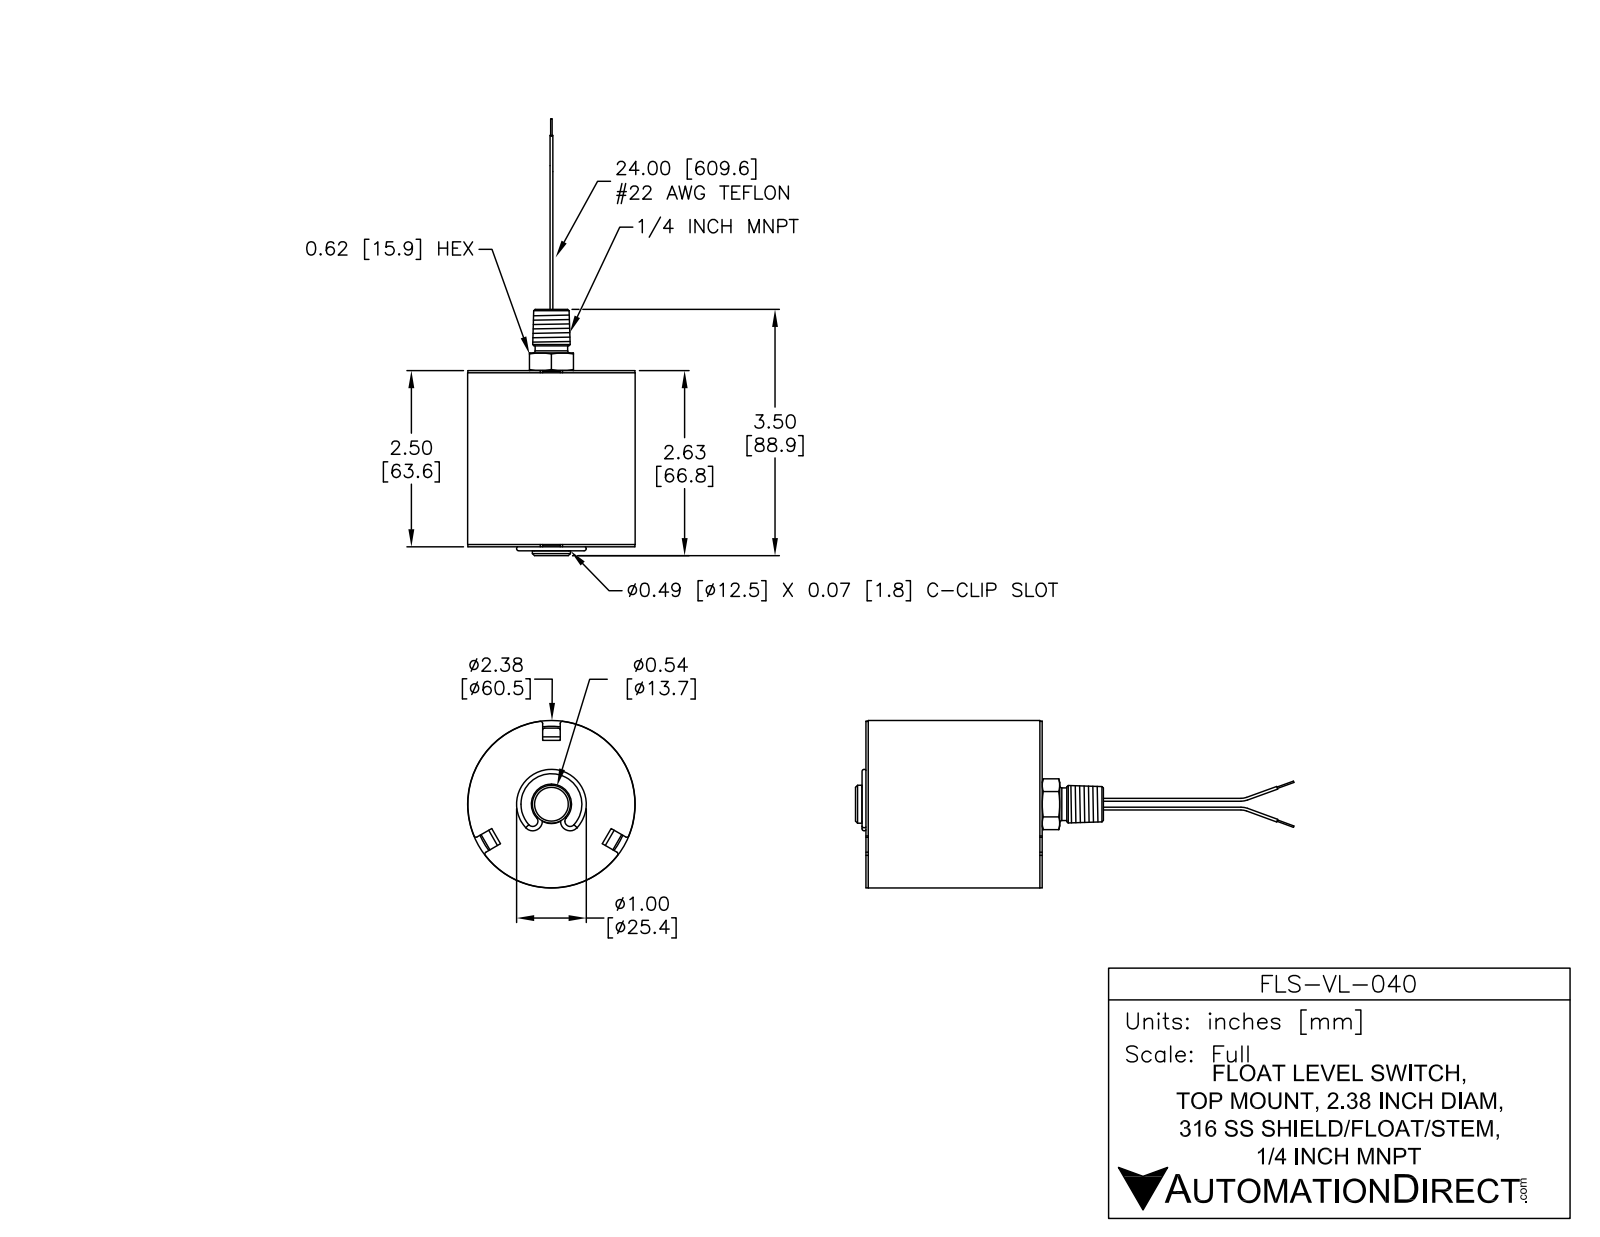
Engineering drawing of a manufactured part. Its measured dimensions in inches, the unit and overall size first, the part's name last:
Units: inches
Overall size (bounding box): 6.289 × 2.375 × 2.375
Round holes (diameter × count): ⌀2.245 ×1
Round bosses / shafts (diameter × count): ⌀0.04 ×4, ⌀0.02 ×2, ⌀2.375 ×1, ⌀2.2 ×1, ⌀0.46 ×1, ⌀0.313 ×1, ⌀0.313 ×1, ⌀0.25 ×1
Main face-to-face distances: 2.439, 0.062, 2.501, 2.376, 0.062, 2.439, 2.377, 2.377, 2.435, 2.374
Volume: 2.125 in³ · Surface area: 60.91 in²
Bodies: 8 solids, 155 faces (75 planar, 44 cylindrical, 36 other)
Part name (STEP PRODUCT): FLS-VL-040
STEP written by: SolidWorks 2013 (AUTOMOTIVE_DESIGN)
